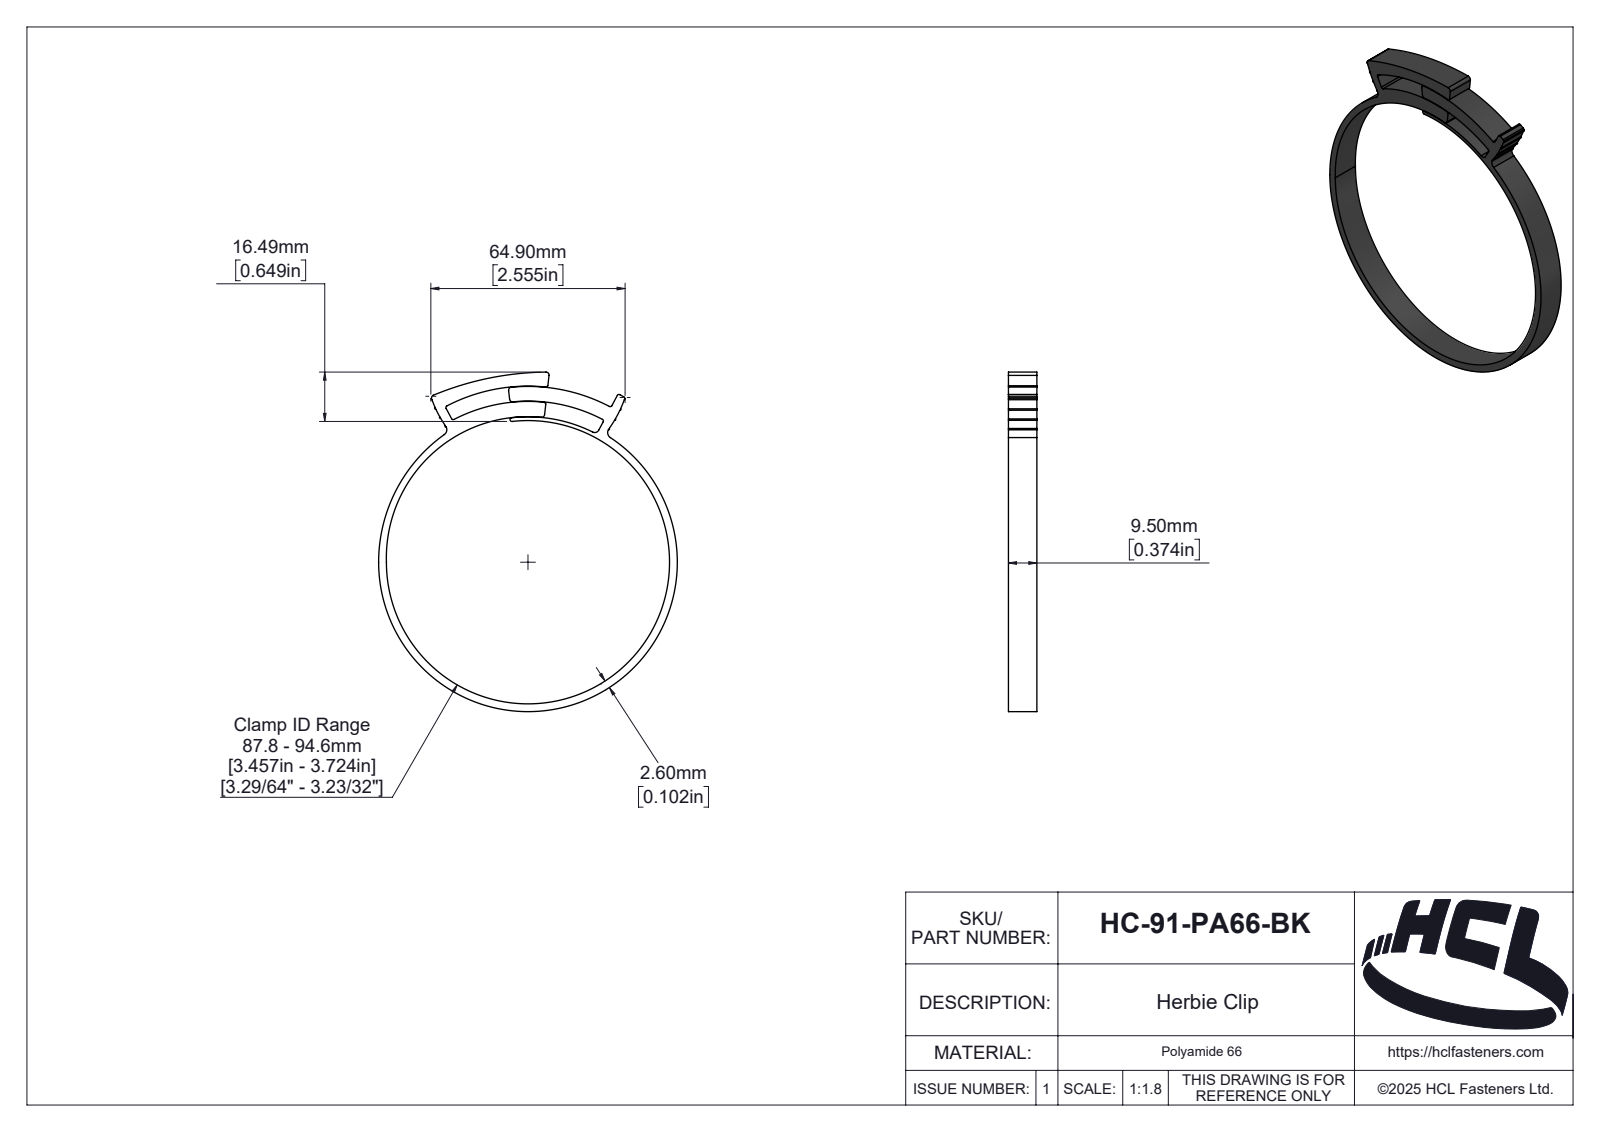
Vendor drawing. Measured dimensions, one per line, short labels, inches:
name: HC-91-PA66-BK
written by: SolidWorks 2025 (AUTOMOTIVE_DESIGN)
unit: in
bodies: 1 solid, 162 faces (13 planar, 100 cylindrical, 49 other)
size: 4.464 × 3.929 × 0.374
volume: 0.732 in³; area: 16.18 in²
rounds: 8× R0.01, 6× R0.024, 5× R0.039, 2× R0.079, 1× R0.007, 1× R0.024, 1× R0.026, 1× R0.033
face distances: 0.374
